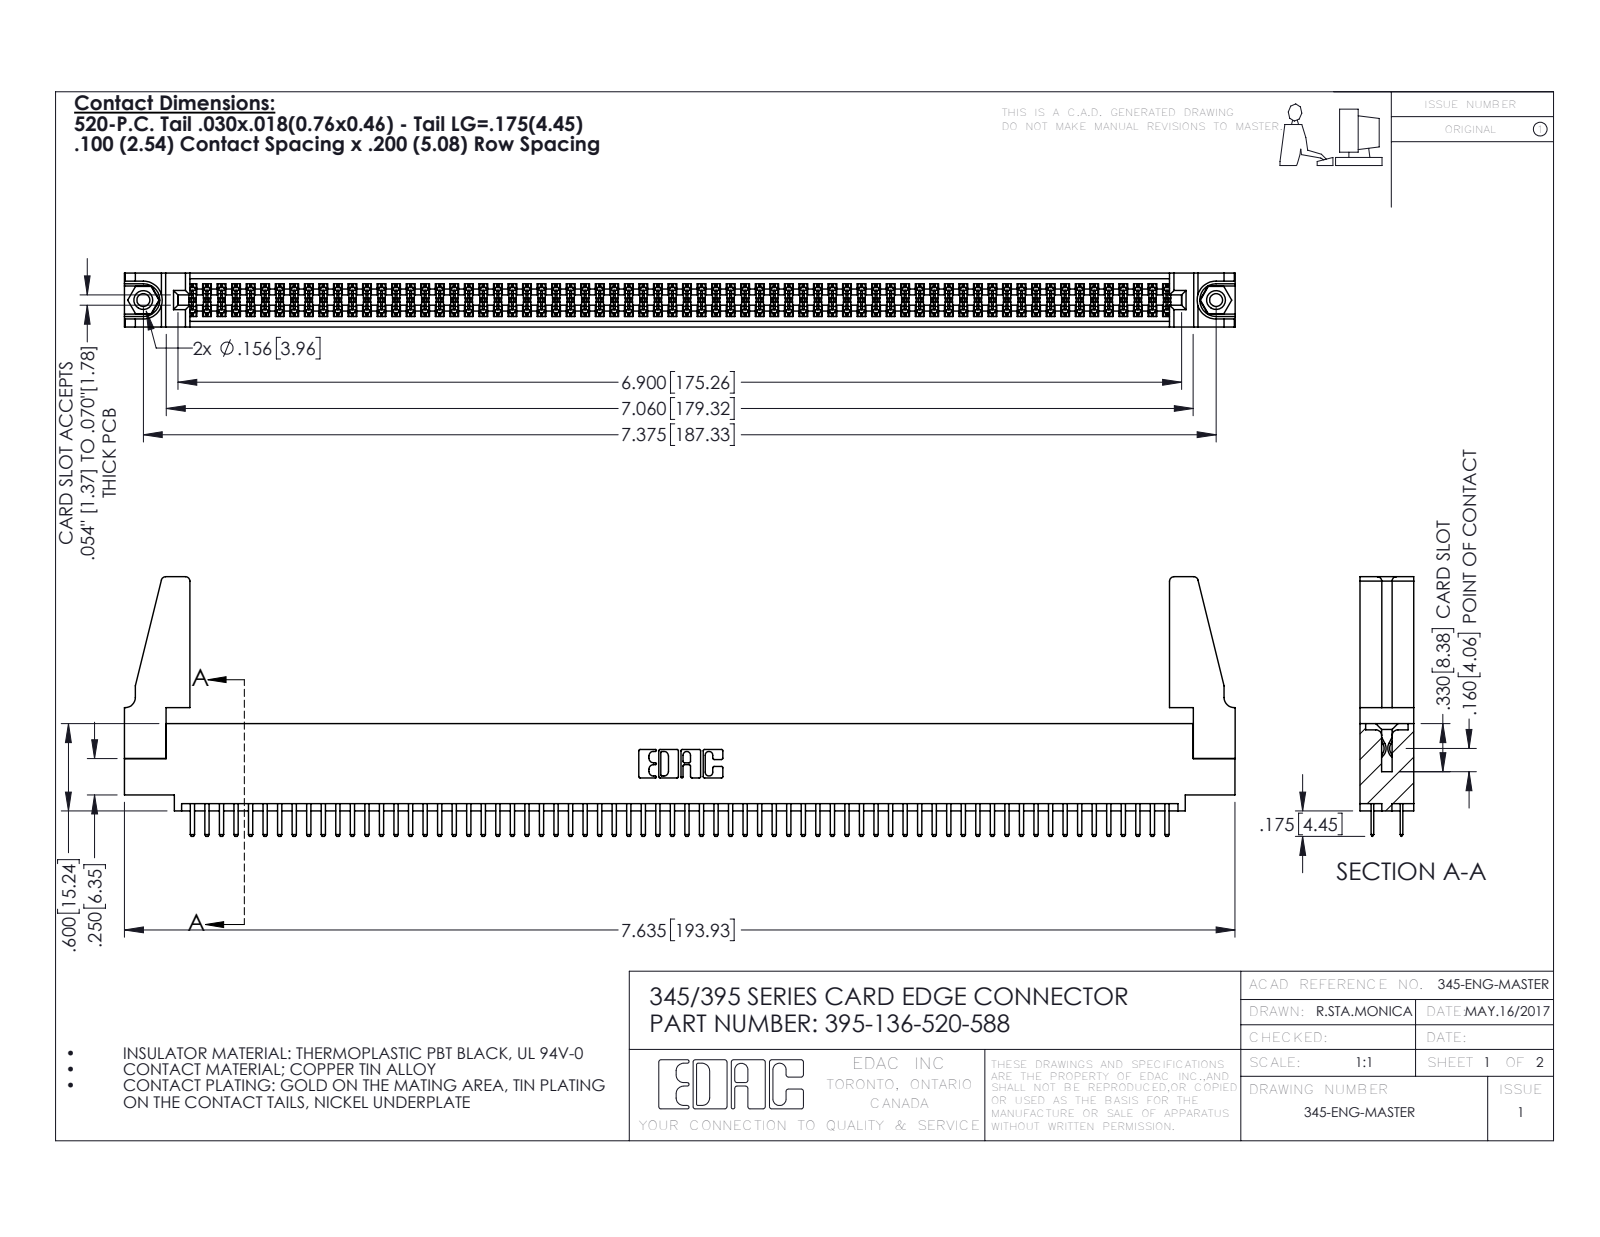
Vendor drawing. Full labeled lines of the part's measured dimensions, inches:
Part name (STEP PRODUCT): 345-220-078_345-220-088; 345 Part_0.110 Offset - 0.156 Dia-TH; 345-292-001_345-293-120; 395-136-520-588 (+1 more)
STEP written by: SolidWorks 2016 (CONFIG_CONTROL_DESIGN)
Units: inches
Bodies: 141 solids, 7598 faces (4916 planar, 2666 cylindrical, 16 other)
Overall size (bounding box): 7.636 × 1.785 × 0.37
Volume: 1.355 in³ · Surface area: 48.98 in²
Round holes (diameter × count): ⌀0.089 ×2, ⌀0.125 ×2, ⌀0.156 ×2, ⌀0.064 ×1
Round bosses / shafts (diameter × count): ⌀0.155 ×2
Partial cylindrical surfaces — rounded edges, fillets, slot ends (radius × count): R0.006 ×204, R0.01 ×140, R0.01 ×22, R0.03 ×8, R0.007 ×6, R0.031 ×6, R0.026 ×3, R0.014 ×2
Main face-to-face distances: 0.072, 0.298, 0.37, 0.2, 0.098, 0.272, 0.025, 0.225, 0.022, 0.072
Hole centre spacings: 0.27, 7.139, 7.375
